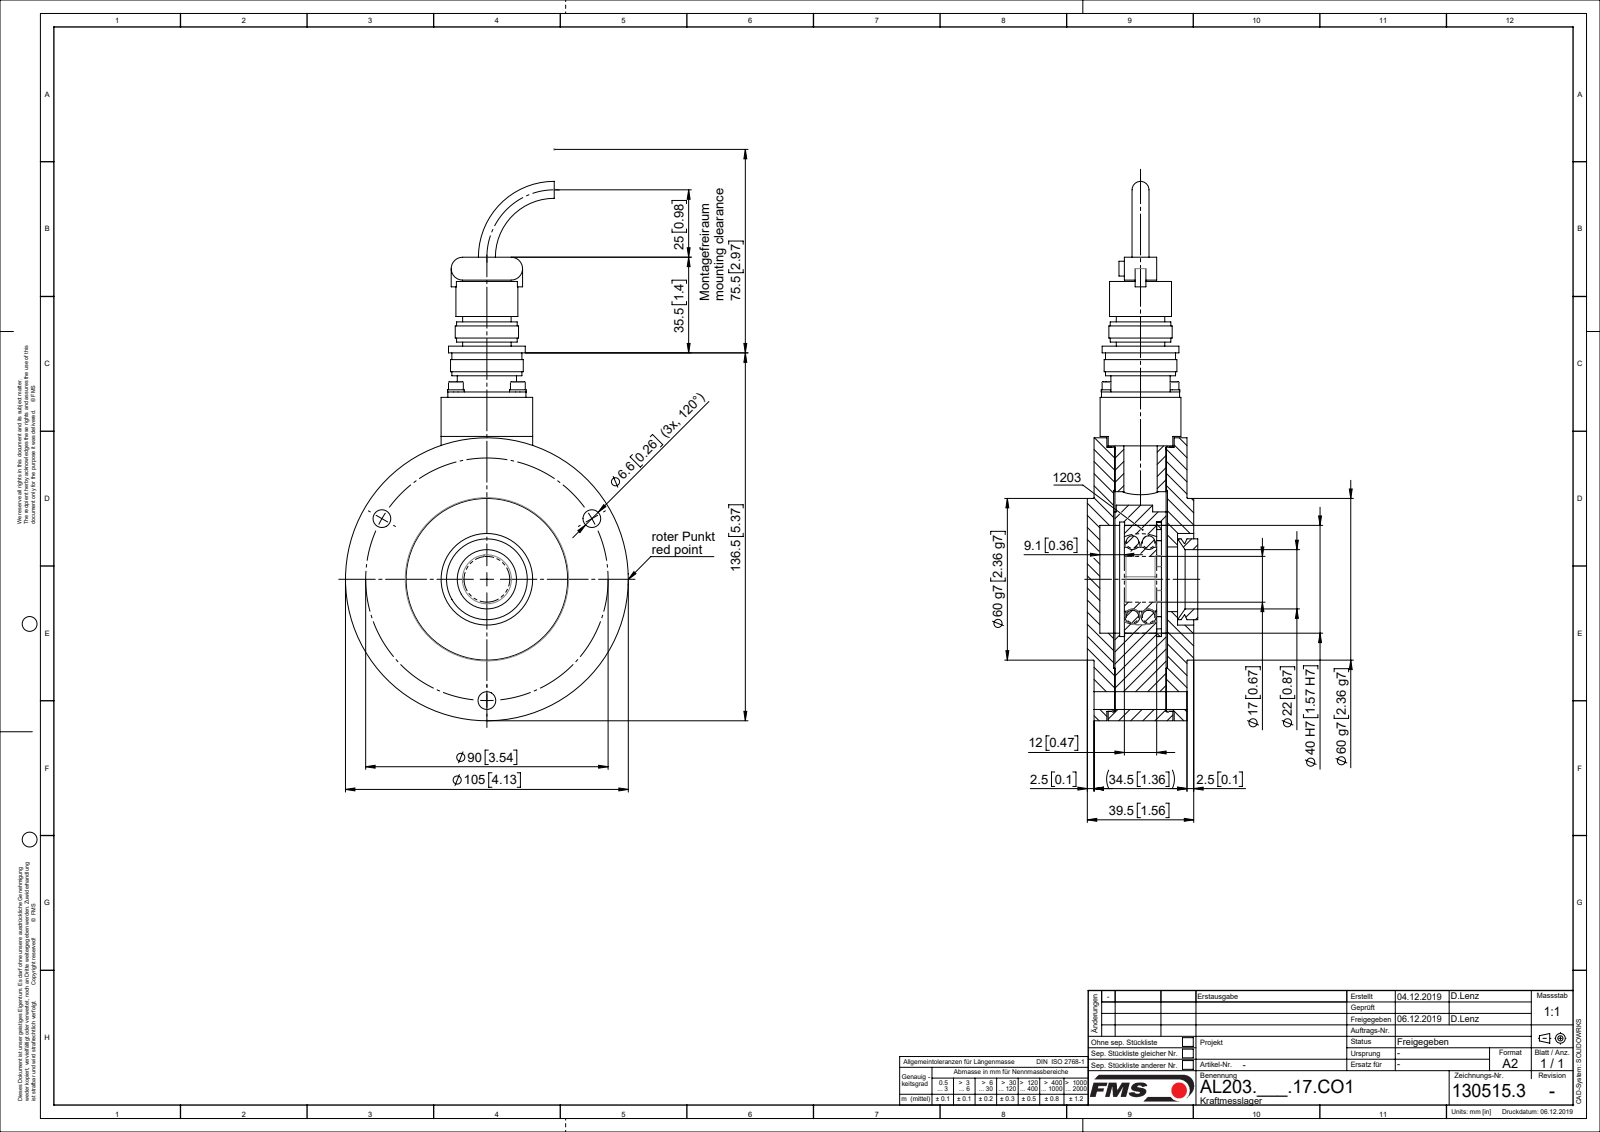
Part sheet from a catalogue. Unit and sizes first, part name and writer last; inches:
Units: inches
Overall size (bounding box): 7.88 × 4.134 × 1.614
Round holes (diameter × count): ⌀0.26 ×10, ⌀0.098 ×8, ⌀0.122 ×4, ⌀0.134 ×4, ⌀0.126 ×2, ⌀0.236 ×2, ⌀0.157 ×1, ⌀0.512 ×1, ⌀0.669 ×1, ⌀0.787 ×1, ⌀0.866 ×1, ⌀0.945 ×1
Round bosses / shafts (diameter × count): ⌀0.217 ×8, ⌀0.118 ×6, ⌀0.244 ×4, ⌀0.098 ×4, ⌀4.134 ×1, ⌀2.362 ×1, ⌀1.181 ×1, ⌀1.122 ×1
Partial cylindrical surfaces — rounded edges, fillets, slot ends (radius × count): R0.004 ×4, R0.147 ×2, R0.167 ×2, R0.608 ×1, R0.726 ×1
Main face-to-face distances: 0.305, 1.053, 0.098, 0.748, 0.285, 0.02, 1.152, 1.171, 1.358, 1.073
Hole centre spacings: 1.772, 3.069, 0.459, 0.515, 0.64, 0.698, 0.906, 1.083
Volume: 18.75 in³ · Surface area: 155.5 in²
Bodies: 43 solids, 506 faces (154 planar, 220 cylindrical, 132 other)
Part name (STEP PRODUCT): Federringe_DIN127A_M03; 130419.4_01; 130515.3_stp; 121207.7_01 (+8 more)
STEP written by: SolidWorks 2018 (CONFIG_CONTROL_DESIGN)
